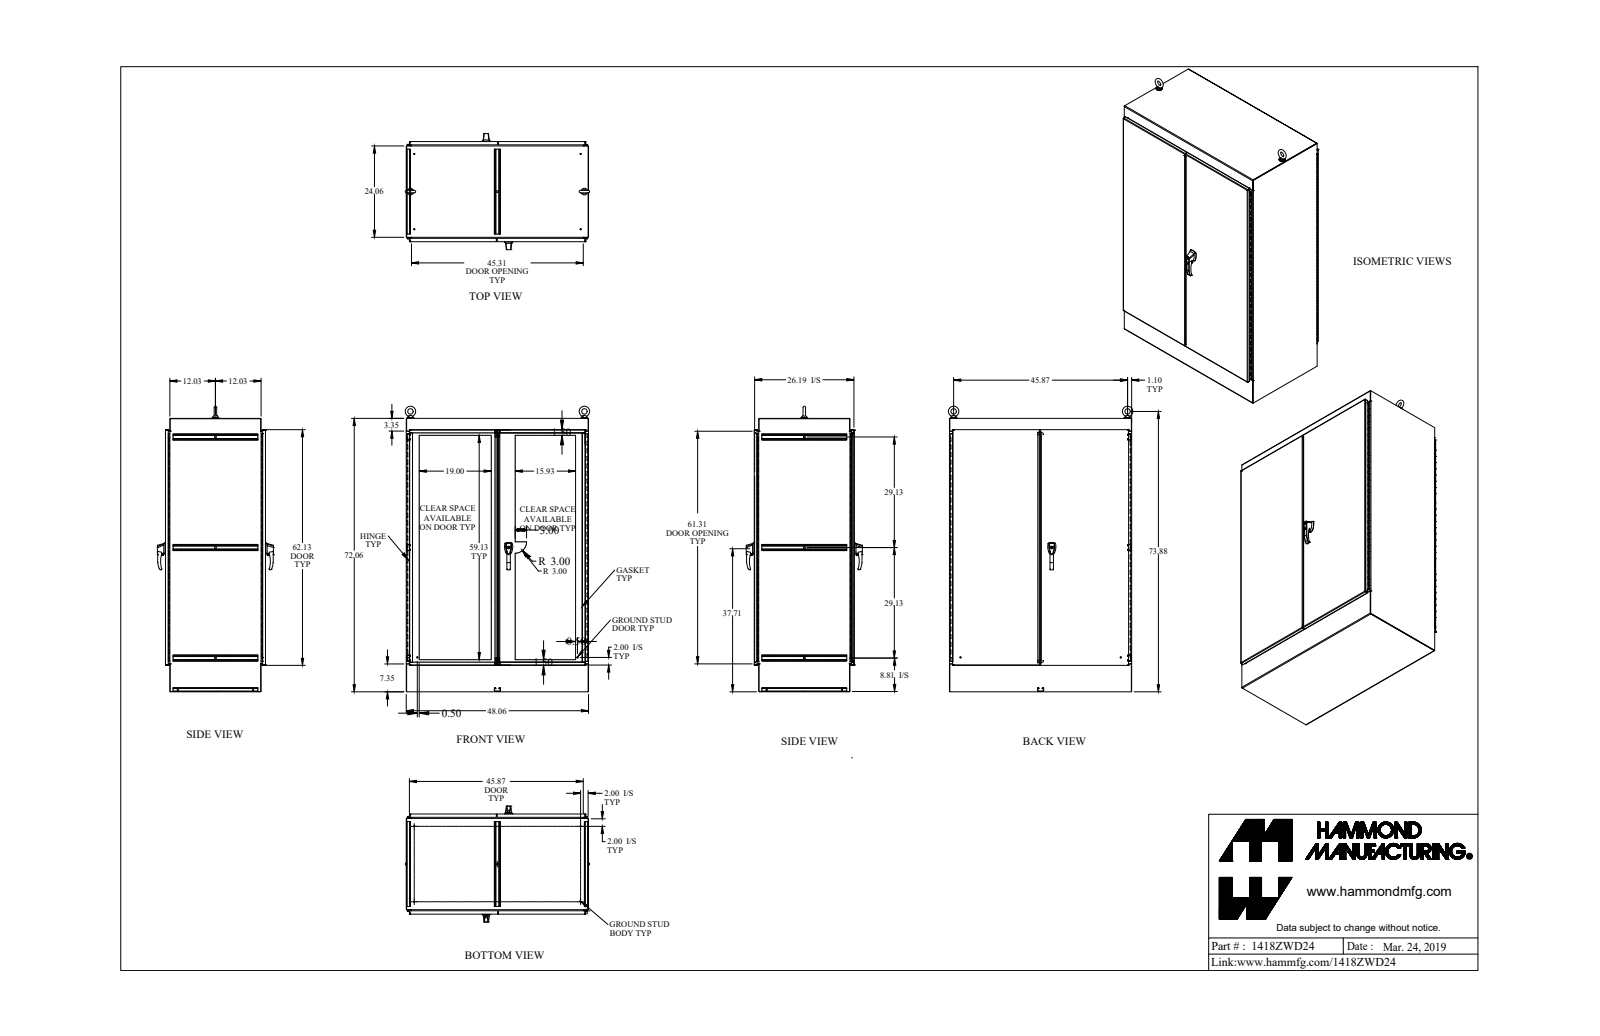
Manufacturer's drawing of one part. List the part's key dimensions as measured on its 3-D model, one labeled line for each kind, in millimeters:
Part name (STEP PRODUCT): 1418ZWD24_Default
STEP written by: SolidWorks 2019 (CONFIG_CONTROL_DESIGN)
Units: millimetres
Bodies: 110 solids, 4540 faces (2062 planar, 2212 cylindrical, 266 other)
Overall size (bounding box): 1923.1 × 1247.6 × 777.6
Volume: 26 250 000 mm³ · Surface area: 21 280 000 mm²
Round holes (diameter × count): ⌀7.7 ×40, ⌀12.7 ×5, ⌀2.8 ×4, ⌀6.4 ×4, ⌀6.5 ×4, ⌀7.1 ×4, ⌀7.1 ×4, ⌀8 ×4, ⌀9.9 ×4, ⌀10.5 ×4, ⌀4.4 ×2, ⌀5.9 ×2
Round bosses / shafts (diameter × count): ⌀7.1 ×12, ⌀6.4 ×8, ⌀25.4 ×4, ⌀19.1 ×4, ⌀16 ×4, ⌀15.9 ×4, ⌀11.2 ×4, ⌀9.4 ×4
Partial cylindrical surfaces — rounded edges, fillets, slot ends (radius × count): R1.1 ×54, R3.5 ×48, R3.2 ×44, R1.2 ×42, R3.6 ×42, R0.5 ×32, R1.3 ×16, R1.5 ×16
Main face-to-face distances: 2.4, 2.4, 667.7, 1218.3, 665.3, 670.2, 1827.9, 1215.9, 1220.7, 29.5
Hole centre spacings: 152.4, 304.8, 1186.6, 1215.6, 457.2, 1262.5, 609.6, 1325.3
